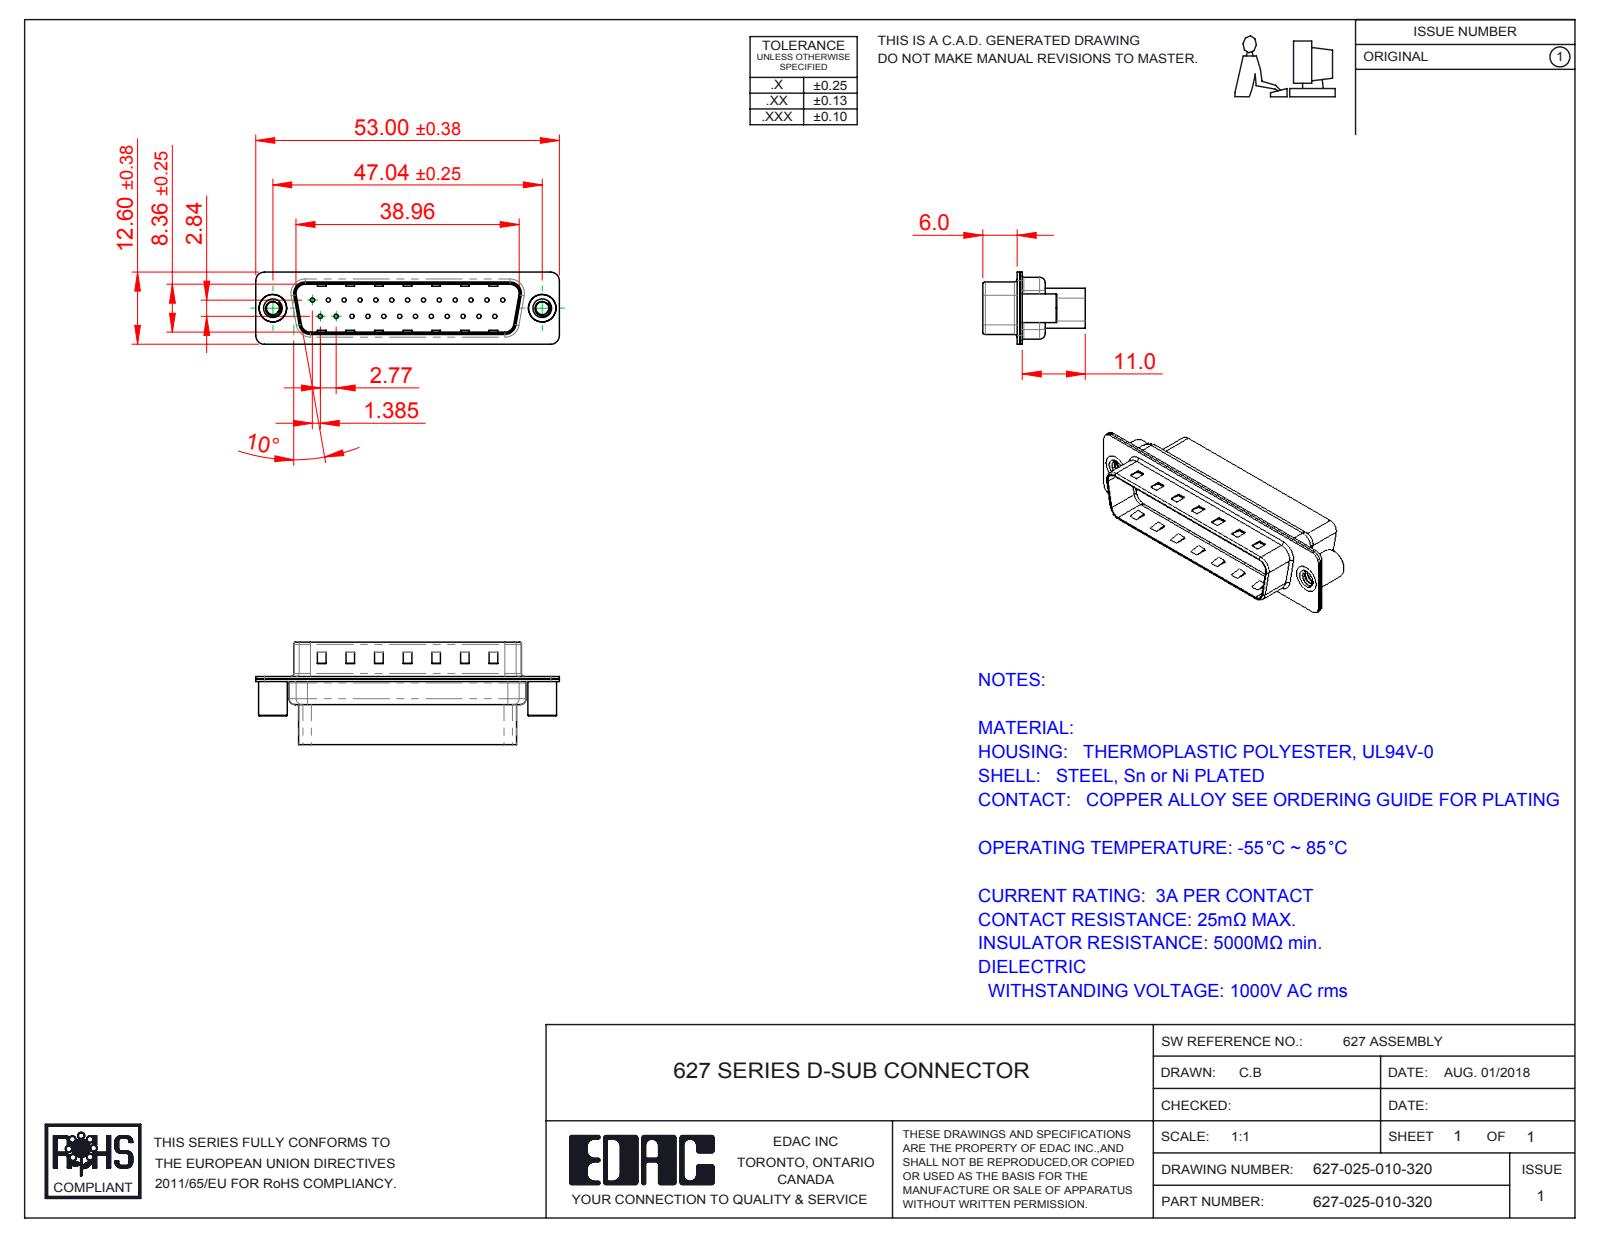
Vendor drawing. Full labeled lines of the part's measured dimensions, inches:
Part name (STEP PRODUCT): 627 Shell Rear_25 Contacts; 627-025-010-320; 627 4-40 Threaded Standoff BS; 627 Shell Front_25 Contacts (+1 more)
STEP written by: SolidWorks 2016 (CONFIG_CONTROL_DESIGN)
Units: inches
Bodies: 5 solids, 598 faces (221 planar, 307 cylindrical, 70 other)
Overall size (bounding box): 2.087 × 0.705 × 0.496
Volume: 0.226 in³ · Surface area: 10.72 in²
Round holes (diameter × count): ⌀0.03 ×25, ⌀0.063 ×25, ⌀0.079 ×25, ⌀0.089 ×2, ⌀0.157 ×2, ⌀0.189 ×2
Round bosses / shafts (diameter × count): ⌀0.197 ×2, ⌀0.193 ×2
Partial cylindrical surfaces — rounded edges, fillets, slot ends (radius × count): R0.059 ×16, R0.079 ×12, R0.02 ×8, R0.063 ×8, R0.01 ×4, R0.024 ×4, R0.026 ×4, R0.035 ×4
Main face-to-face distances: 0.016, 0.018, 0.032, 0.377, 0.027, 0.302, 0.035, 0.043, 0.318, 0.345
Hole centre spacings: 0.124, 0.327, 0.109, 0.218, 0.436, 0.654, 0.198, 0.198
